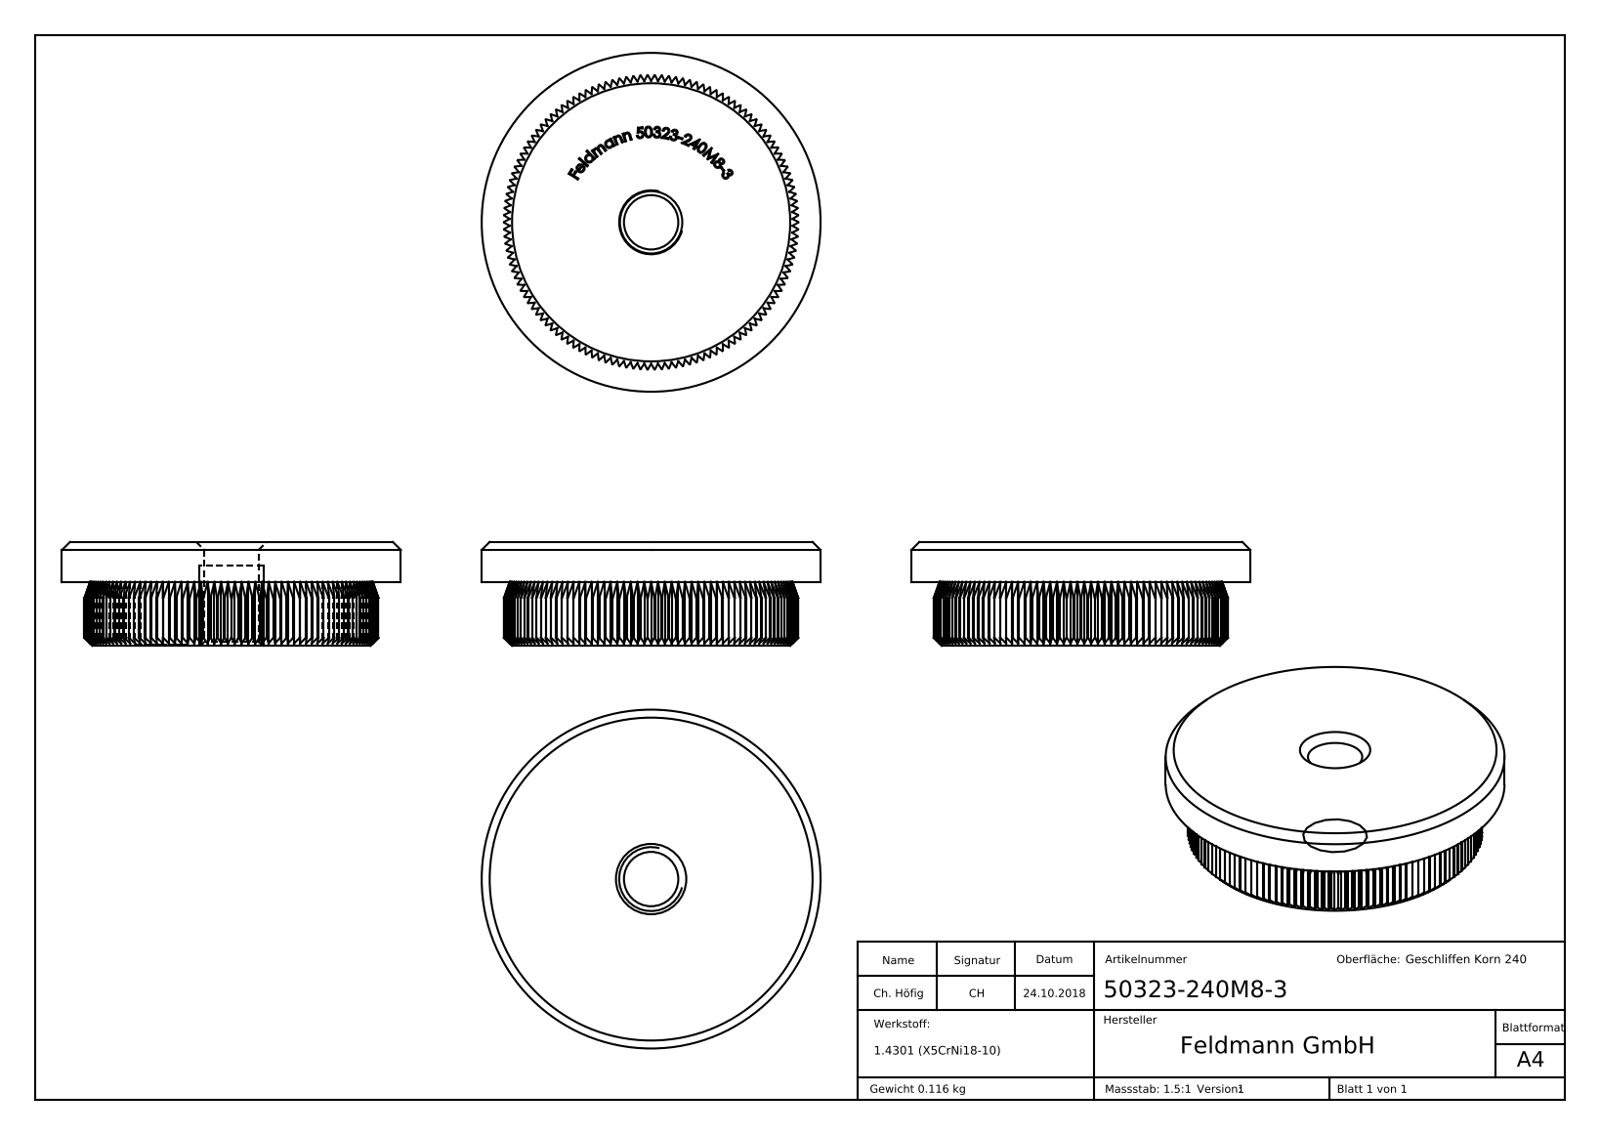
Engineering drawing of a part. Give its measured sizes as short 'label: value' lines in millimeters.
name: 50323-240M8-3
written by: SolidWorks 2015 (CONFIG_CONTROL_DESIGN)
unit: mm
bodies: 1 solid, 821 faces (410 planar, 134 cylindrical, 277 other)
size: 42.4 × 42.4 × 13
volume: 14 663 mm³; area: 5 197 mm²
holes: 1× ⌀6.8
bosses: 1× ⌀42.4
rounds: 1× R18.4
face distances: 13, 17.7, 8, 5, 17.72, 17.68, 7.9, 12.9, 0.54, 0.67
